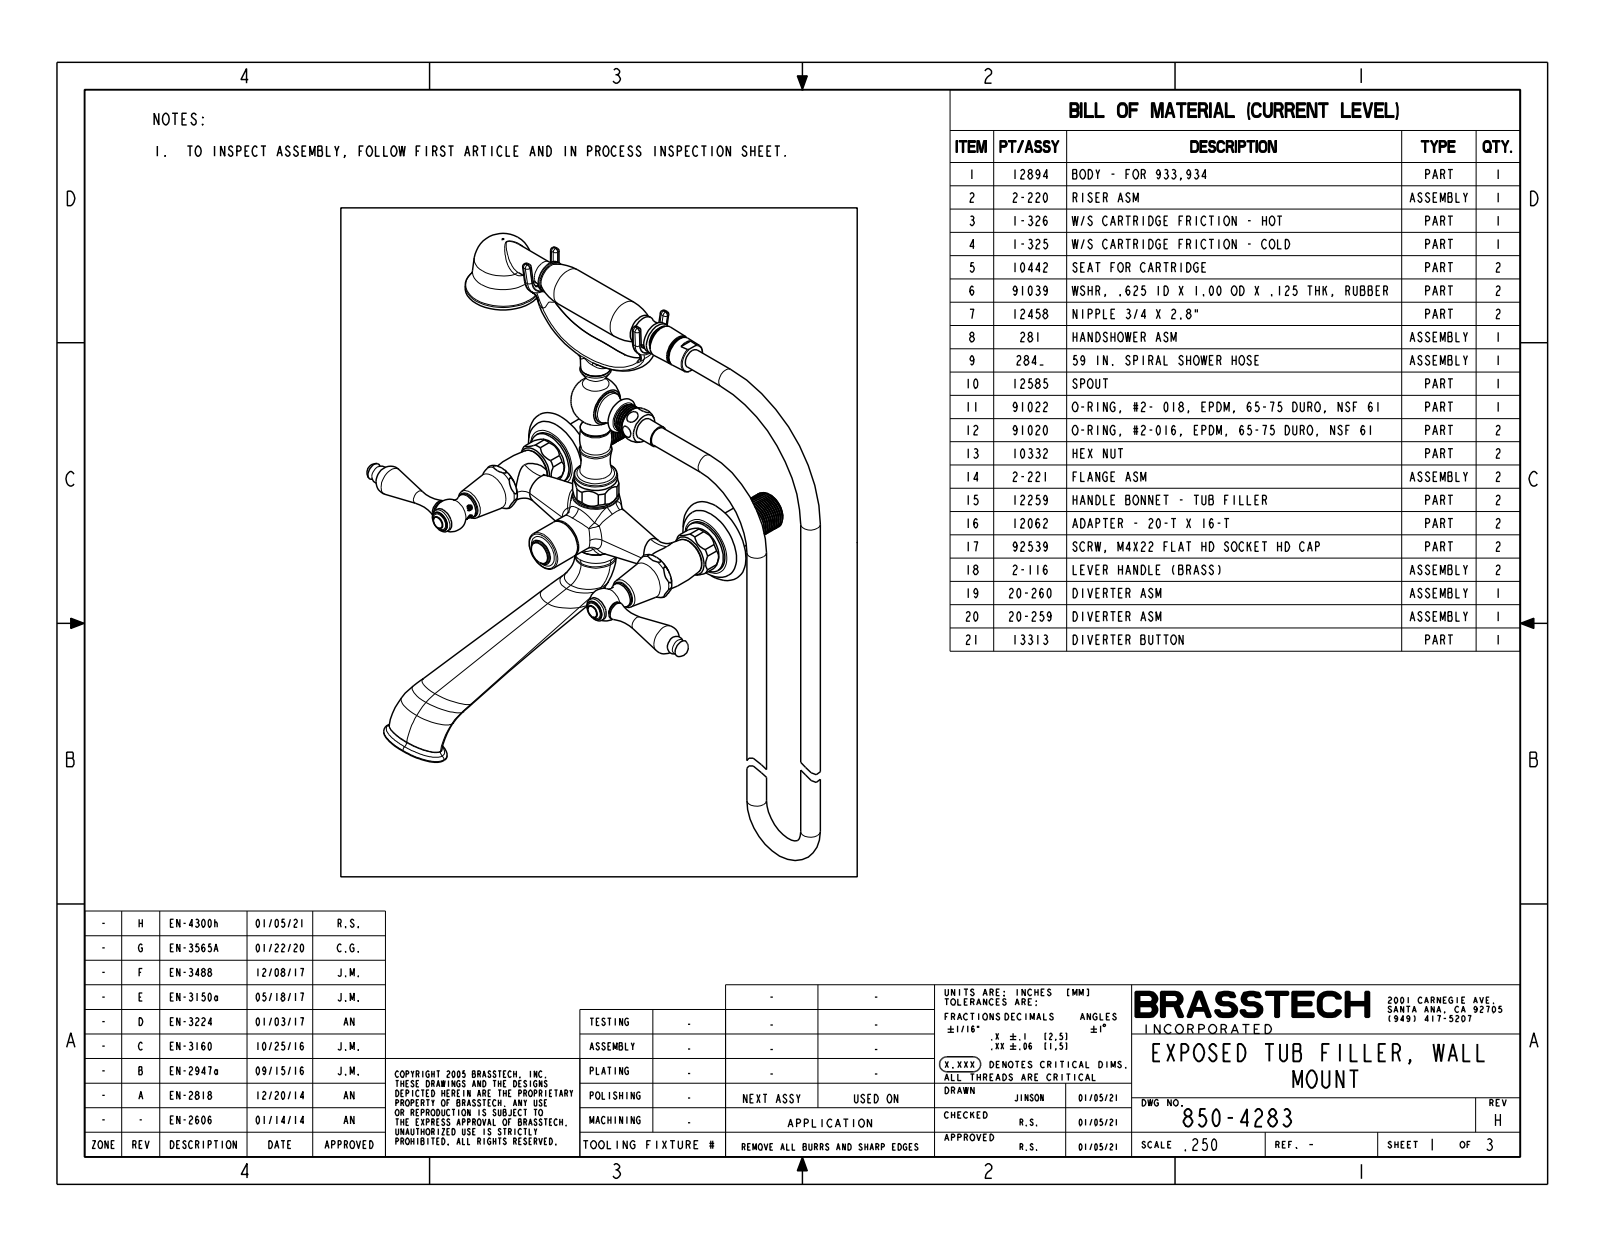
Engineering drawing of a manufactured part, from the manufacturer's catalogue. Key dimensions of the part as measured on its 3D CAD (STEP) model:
Part name (STEP PRODUCT): 850-4283
STEP written by: CREO PARAMETRIC BY PTC INC, 2018400 (CONFIG_CONTROL_DESIGN)
Units: inches
Bodies: 1 solid, 845 faces (179 planar, 239 cylindrical, 427 other)
Overall size (bounding box): 23.86 × 14.41 × 9.14
Volume: 49.58 in³ · Surface area: 264.7 in²
Round holes (diameter × count): ⌀0.046 ×52
Round bosses / shafts (diameter × count): ⌀0.82 ×4, ⌀0.54 ×4, ⌀1.482 ×2, ⌀0.705 ×2, ⌀0.661 ×2, ⌀0.544 ×2, ⌀0.4 ×2, ⌀2.08 ×1
Partial cylindrical surfaces — rounded edges, fillets, slot ends (radius × count): R0.085 ×32, R0.637 ×3, R0.595 ×2, R0.405 ×1, R0.406 ×1, R0.45 ×1
Main face-to-face distances: 1.188, 3, 0.437, 0.58, 1.017, 4.188, 1.812, 0.642, 10.058, 0.375
Hole centre spacings: 0.187, 0.367, 0.535, 0.813, 1.021, 0.184, 0.601, 0.685
